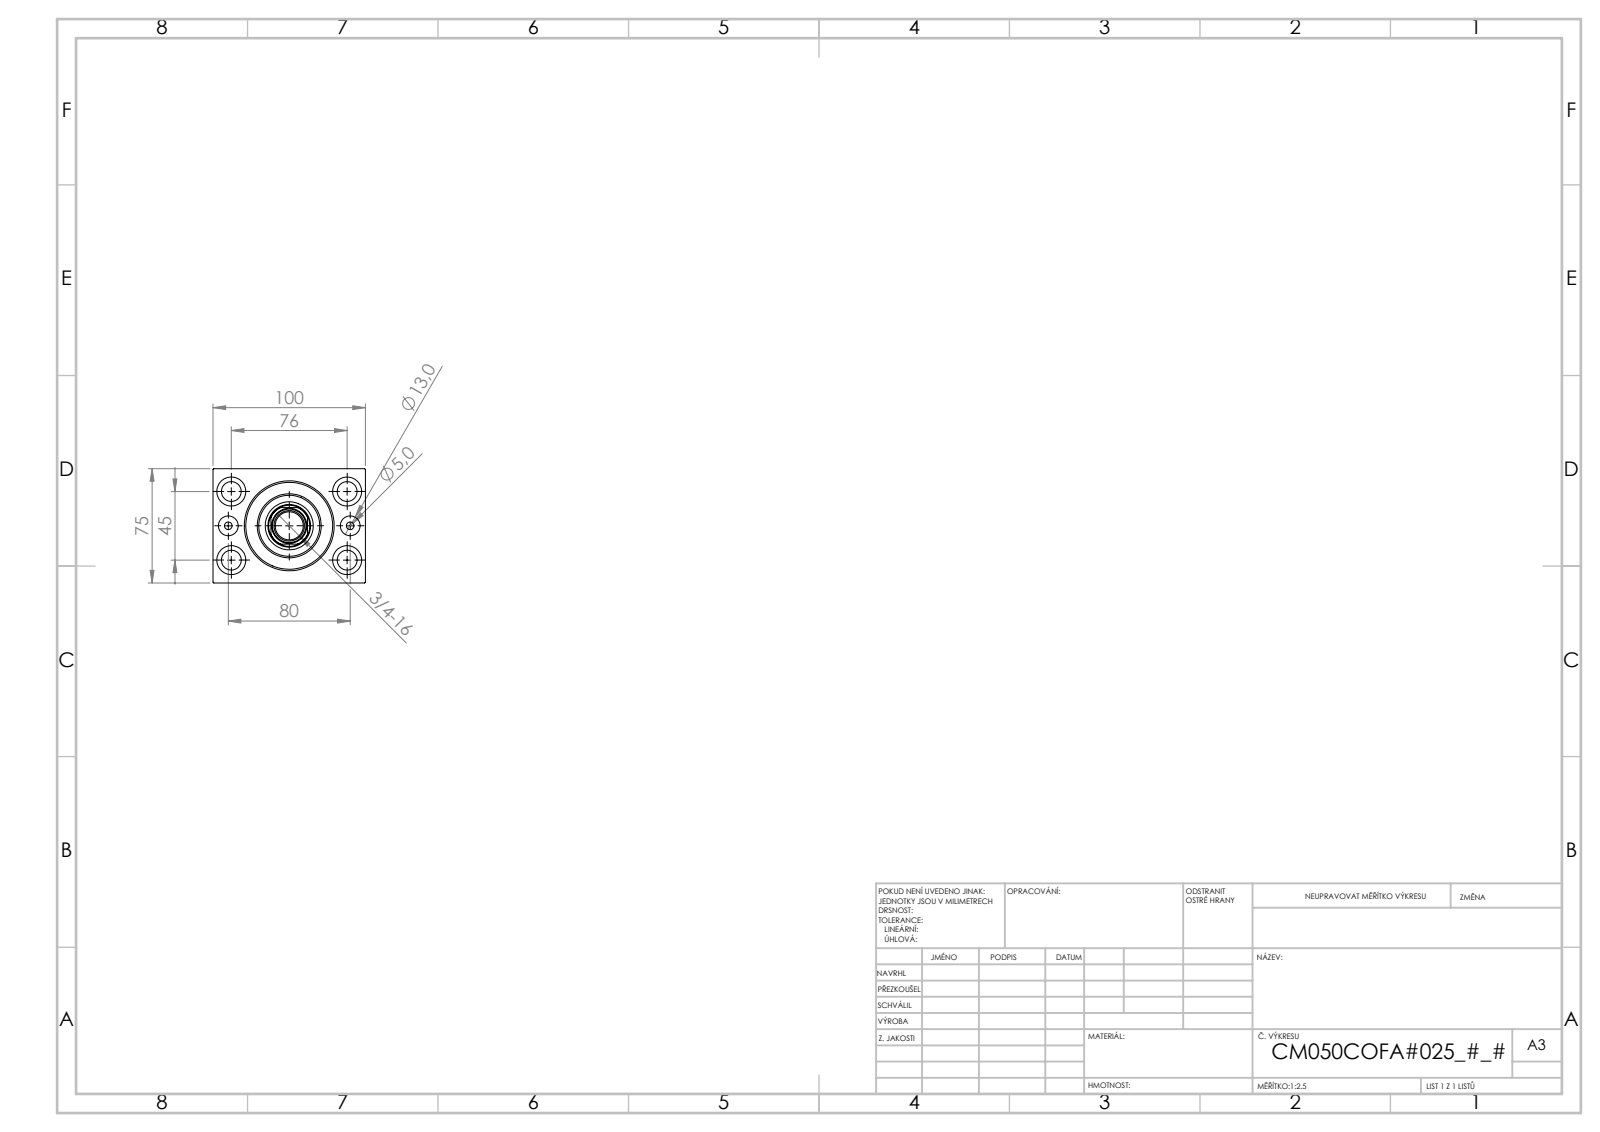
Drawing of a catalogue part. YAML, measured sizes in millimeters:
part_name: "V450CM_MALE_METRIC; V450CM_VC_B; V450CM_C_VCP; V450CM_C_Body"
step_written_by: "SolidWorks 2019 (CONFIG_CONTROL_DESIGN)"
units: millimeters
bodies: {solids: 4, faces: 875, planar: 413, cylindrical: 62, other: 400}
overall_size: [140, 100, 75]
volume: 638796
surface_area: 110002
round_holes:
  - {diameter: 13, count: 6}
  - {diameter: 19, count: 4}
  - {diameter: 5, count: 2}
  - {diameter: 18.5, count: 1}
  - {diameter: 28, count: 1}
  - {diameter: 31.5, count: 1}
  - {diameter: 50, count: 1}
  - {diameter: 52, count: 1}
  - {diameter: 57, count: 1}
round_bosses_or_shafts:
  - {diameter: 42, count: 1}
  - {diameter: 20, count: 1}
  - {diameter: 18, count: 1}
partial_cylinders:
  - {radius: 13.5, count: 1}
face_to_face_distances: [75, 100, 98, 84, 14, 12, 72, 25, 86, 47]
hole_center_spacings: [22.59, 44.16, 81.18, 40, 45, 76, 88.32, 80]
